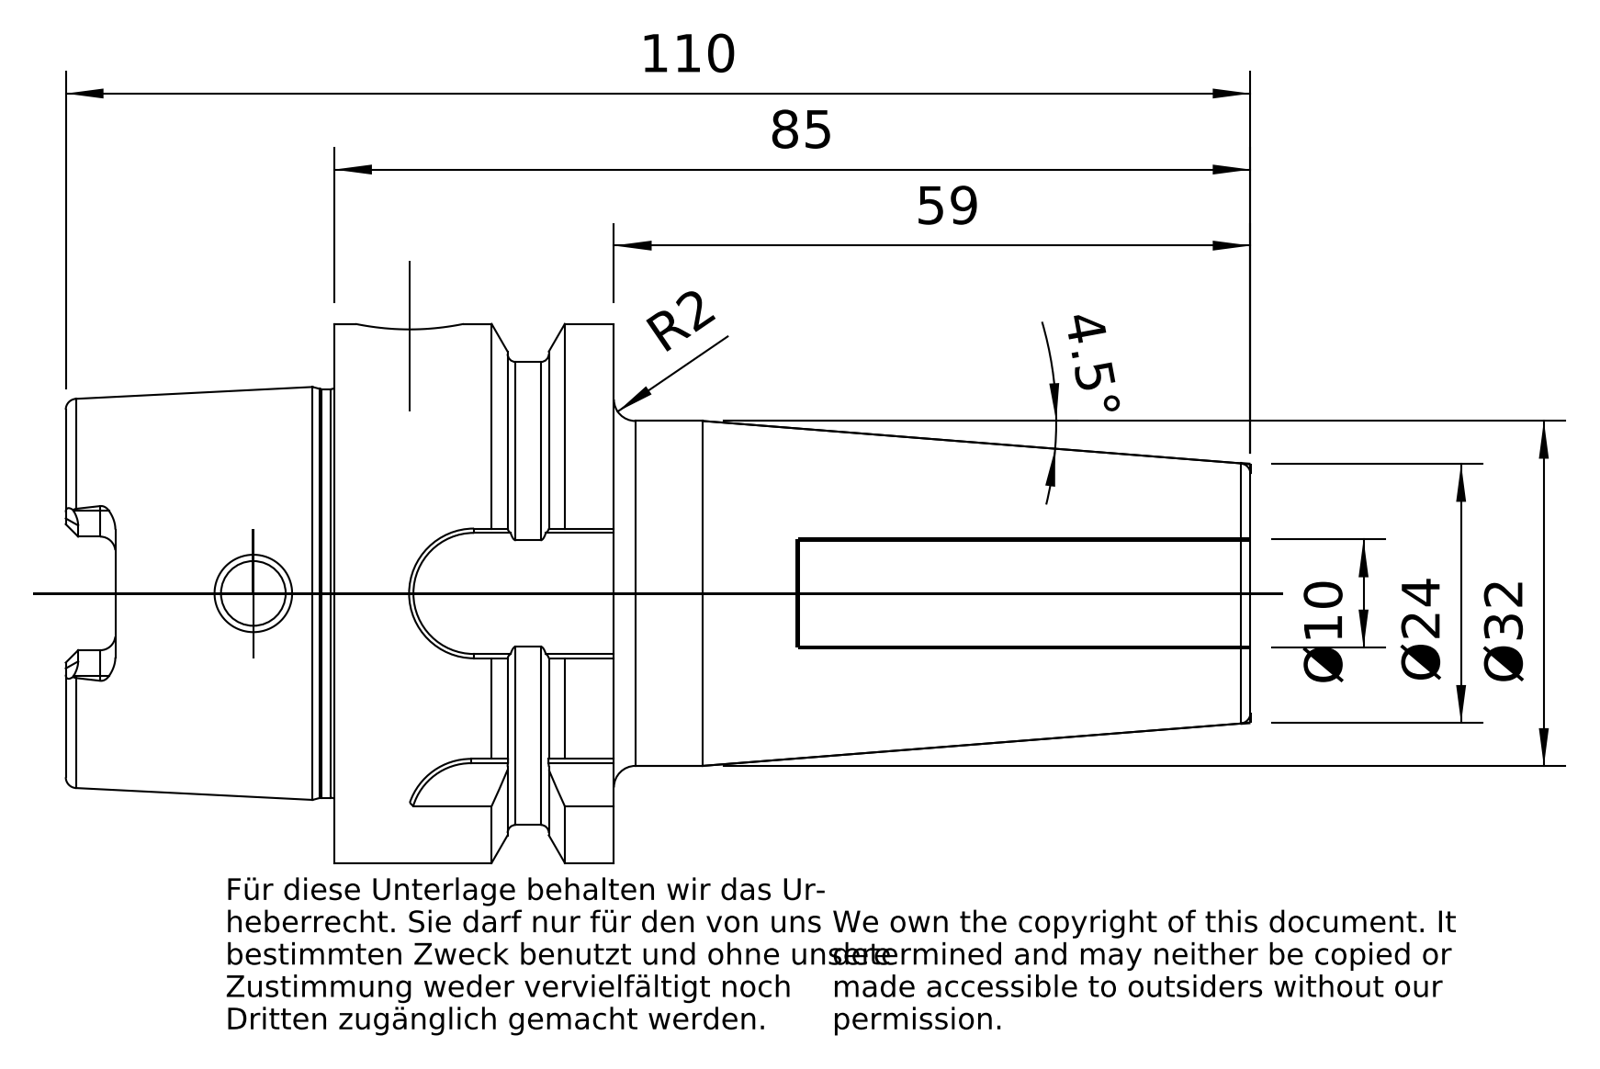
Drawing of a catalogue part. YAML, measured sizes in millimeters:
part_name: "A50-140-10"
step_written_by: "PRO/ENGINEER BY PARAMETRIC TECHNOLOGY CORPORATION, 2010430 (CONFIG_CONTROL_DESIGN)"
units: millimeters
bodies: {solids: 1, faces: 184, planar: 63, cylindrical: 49, other: 72}
overall_size: [109.9, 50, 50]
volume: 83767
surface_area: 21478
round_holes:
  - {diameter: 10, count: 2}
  - {diameter: 6, count: 1}
  - {diameter: 14, count: 1}
  - {diameter: 16, count: 1}
  - {diameter: 16.32, count: 1}
  - {diameter: 16.5, count: 1}
  - {diameter: 26.04, count: 1}
  - {diameter: 32.08, count: 1}
round_bosses_or_shafts:
  - {diameter: 50, count: 1}
  - {diameter: 42.95, count: 1}
  - {diameter: 37.91, count: 1}
  - {diameter: 32, count: 1}
partial_cylinders:
  - {radius: 1.4, count: 6}
  - {radius: 2.38, count: 4}
  - {radius: 6, count: 3}
  - {radius: 6.02, count: 1}
face_to_face_distances: [25.95, 85, 59.05, 24.9, 50.85, 109.9, 34.85, 9.95, 16, 75.05]
